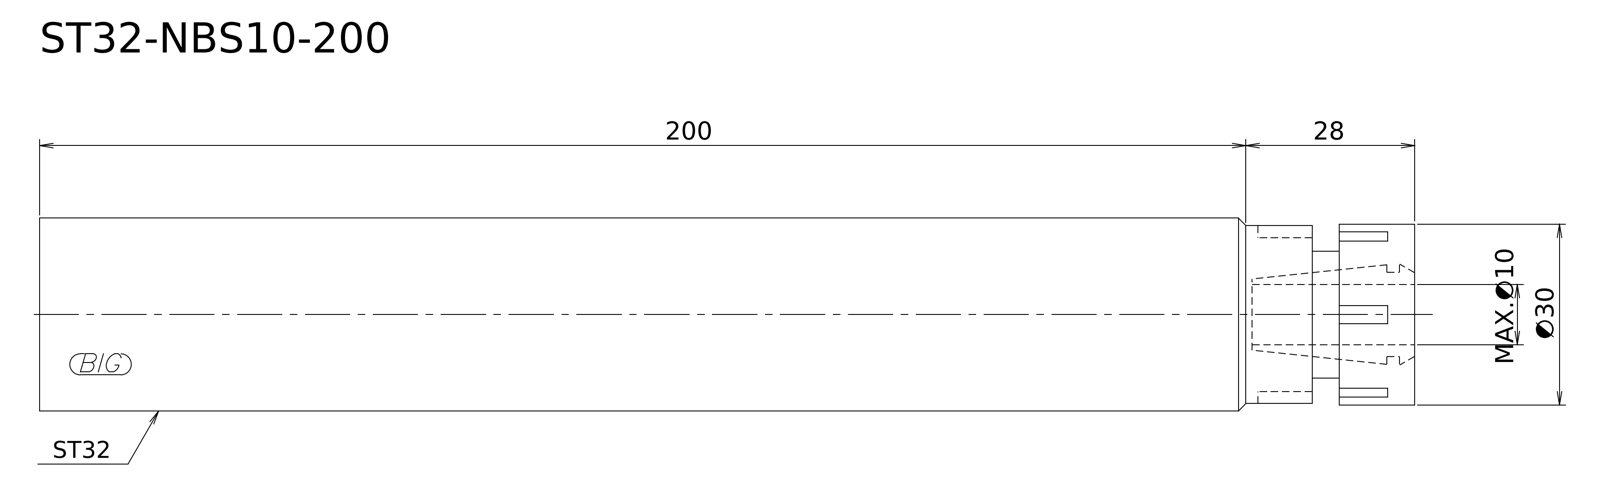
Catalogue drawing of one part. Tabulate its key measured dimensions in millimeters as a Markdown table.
| quantity | value |
| --- | --- |
| STEP written by | Kubotek KeyCreator V8.5.1 (14335) (CONFIG_CONTROL_DESIGN) |
| units | millimeters |
| bodies | 1 solid, 9 faces (4 planar, 4 cylindrical, 1 other) |
| overall size | 228 × 32 × 32 |
| volume | 178 686 mm³ |
| surface area | 24 854 mm² |
| round bosses / shafts (diameter × count) | 32 × 1, 30 × 1, 29.5 × 1, 21 × 1 |
| main face-to-face distances | 228, 12.5, 215.5, 17, 4.5, 211 |
